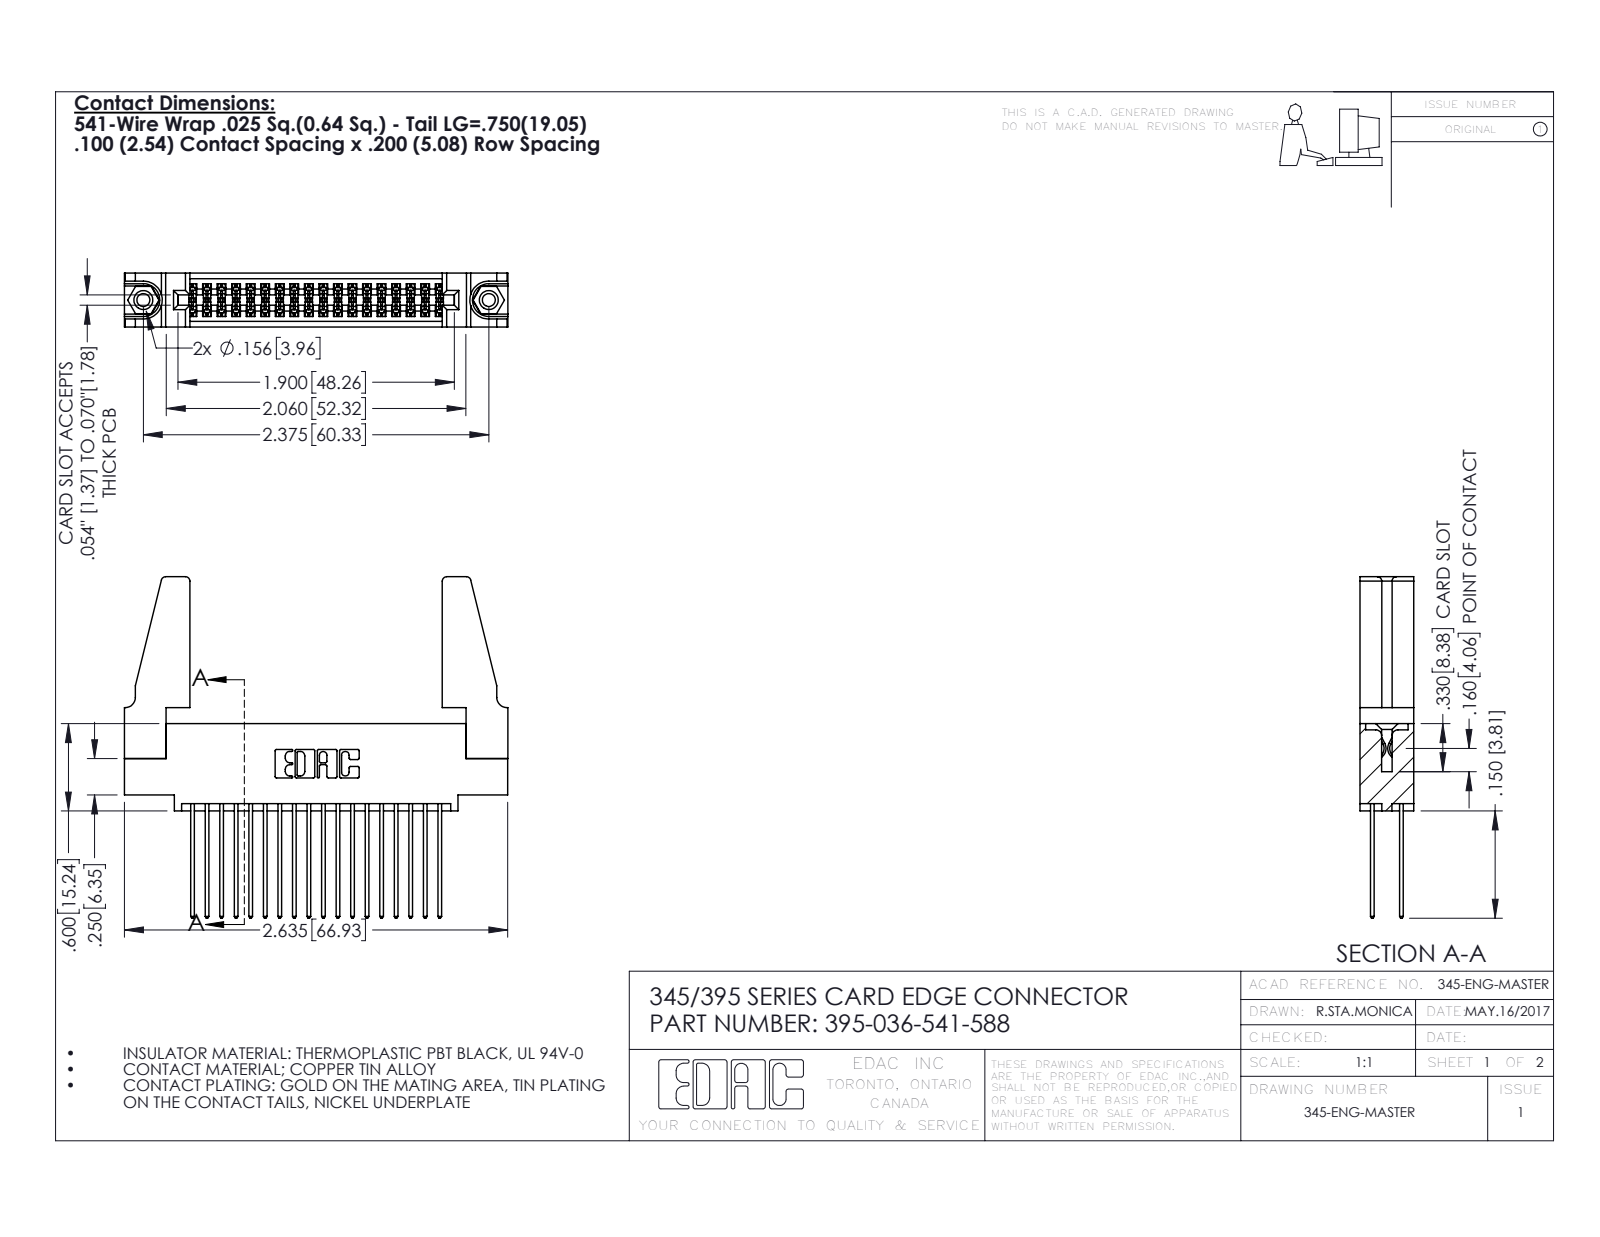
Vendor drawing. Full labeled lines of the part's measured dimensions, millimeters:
Part name (STEP PRODUCT): 345-220-078_345-220-088; 345-292-001_345-293-141; 345 Part_0.110 Offset - 0.156 Dia-TH; 395-036-541-588 (+1 more)
STEP written by: SolidWorks 2016 (CONFIG_CONTROL_DESIGN)
Units: millimetres
Bodies: 41 solids, 2054 faces (1344 planar, 694 cylindrical, 16 other)
Overall size (bounding box): 67 × 59.6 × 9.4
Volume: 9 670 mm³ · Surface area: 13 200 mm²
Round holes (diameter × count): ⌀2.3 ×2, ⌀3.2 ×2, ⌀4 ×2, ⌀1.6 ×1
Round bosses / shafts (diameter × count): ⌀3.9 ×2
Partial cylindrical surfaces — rounded edges, fillets, slot ends (radius × count): R0.2 ×54, R0.3 ×36, R0.3 ×22, R0.8 ×8, R0.2 ×6, R0.8 ×6, R0.7 ×3, R0.4 ×2
Main face-to-face distances: 1.8, 7.6, 9.4, 5.1, 2.5, 6.9, 0.6, 5.7, 4.4, 3.8
Hole centre spacings: 6.9, 54.4, 60.3
